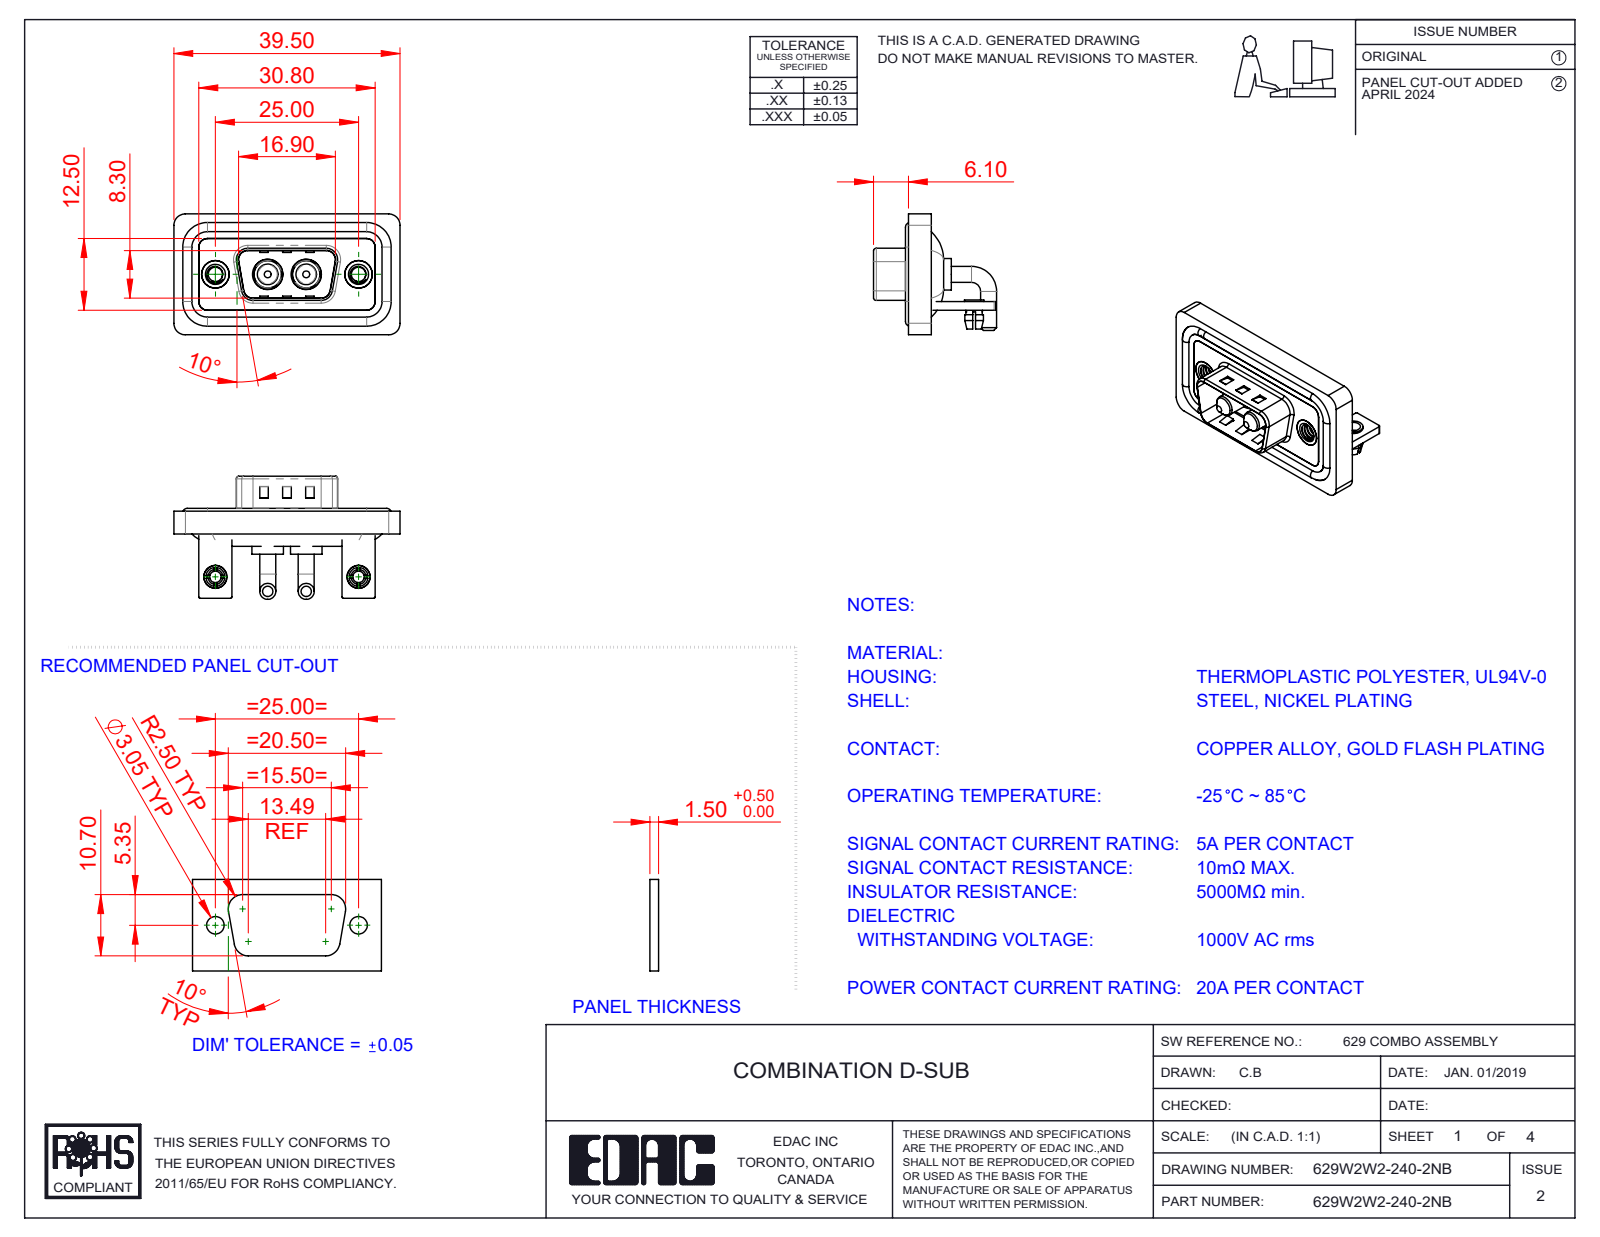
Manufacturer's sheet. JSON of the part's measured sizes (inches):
{"part_name": "629Combo Board Lock; 629W2W2-240-2NB; 629Combo Housing_2W2; 629Combo Waterproof Housing_09 Contacts (+5 more)", "step_written_by": "SolidWorks 2023 (CONFIG_CONTROL_DESIGN)", "units": "inches", "bodies": {"solids": 15, "faces": 627, "planar": 233, "cylindrical": 272, "other": 122}, "overall_size": [1.555, 0.846, 0.831], "volume_in3": 0.299, "surface_area_in2": 12.35, "round_holes": [[0.098, 4], [0.079, 2], [0.126, 2], [0.157, 2], [0.189, 2], [0.191, 2], [0.197, 2], [0.209, 2]], "round_bosses_or_shafts": [[0.11, 4], [0.063, 4], [0.217, 2], [0.205, 2], [0.193, 2], [0.187, 2], [0.157, 2], [0.148, 2]], "partial_cylinders_radius": [[0.079, 19], [0.059, 18], [0.01, 16], [0.02, 9], [0.063, 8], [0.024, 4], [0.026, 4], [0.035, 4]], "face_to_face_distances": [0.016, 0.059, 0.114, 0.031, 0.043, 0.047, 0.083, 0.063, 0.146, 0.098], "hole_center_spacings": [0.36, 0.624, 0.984, 0.265]}
